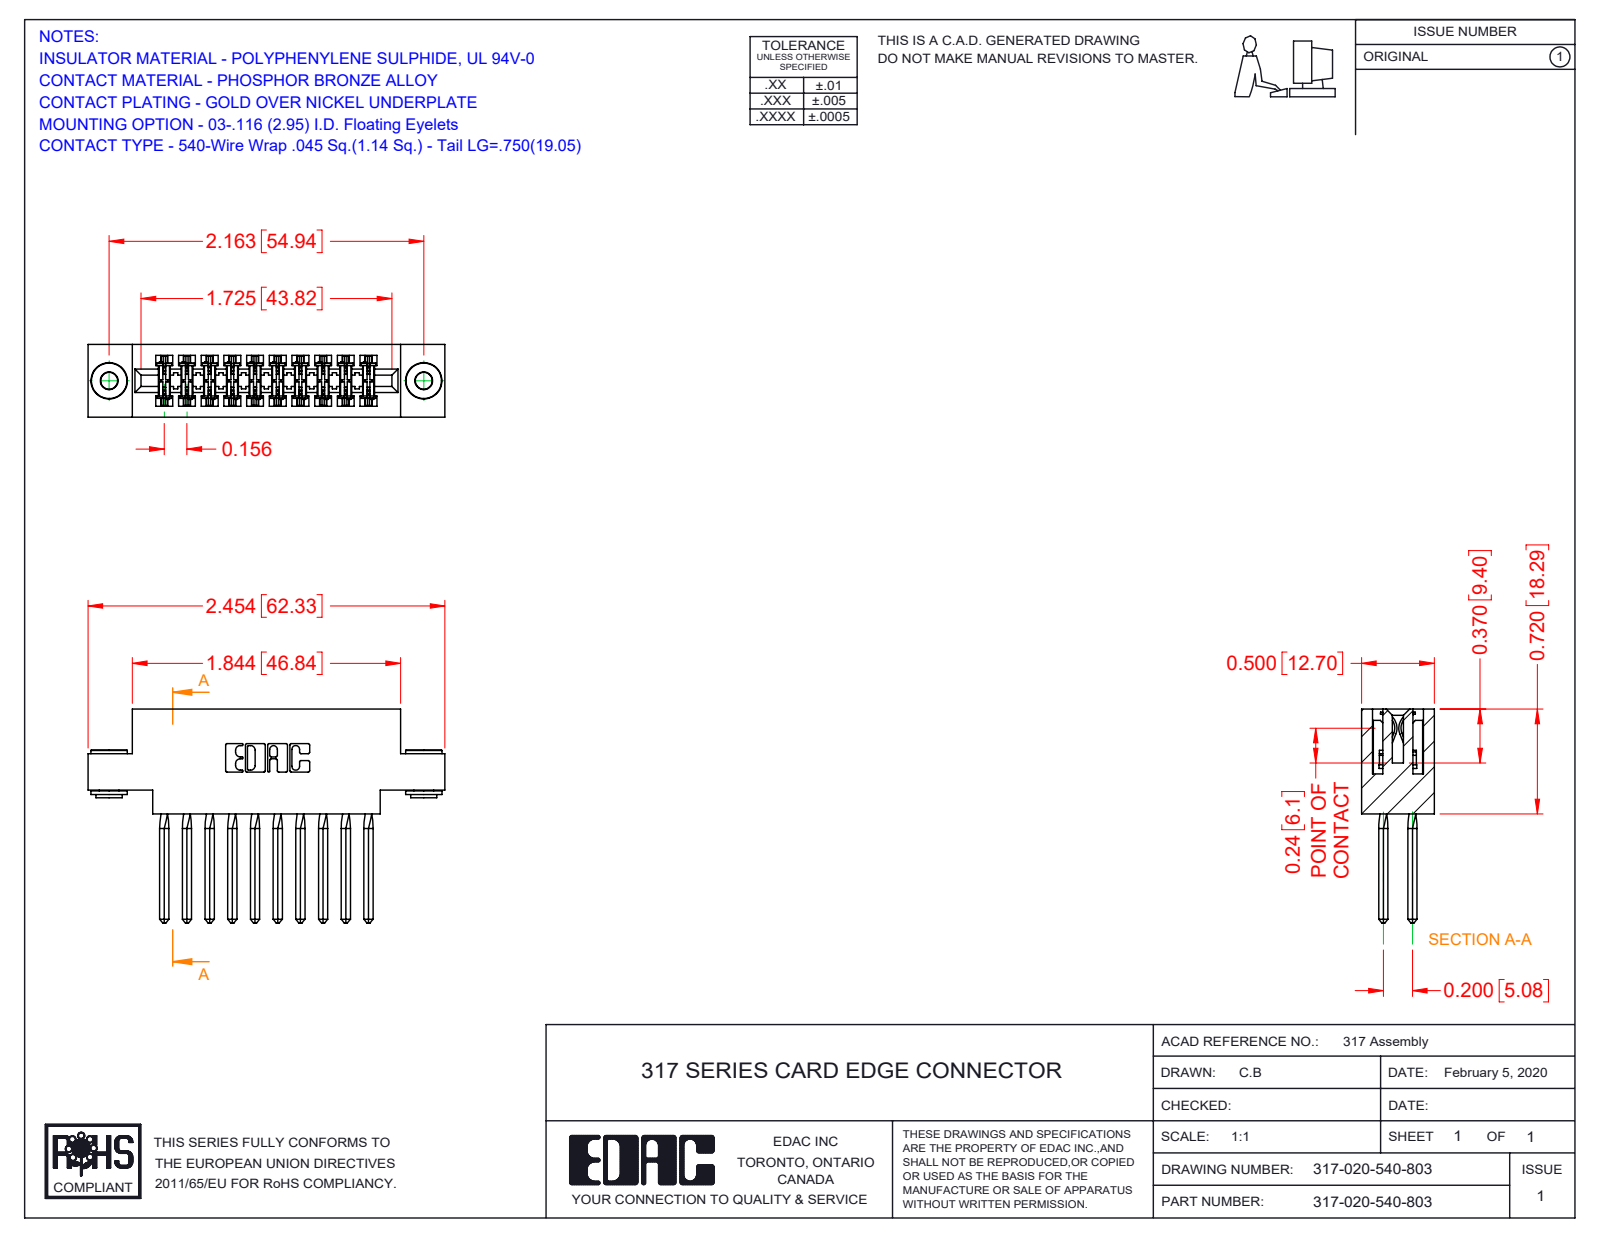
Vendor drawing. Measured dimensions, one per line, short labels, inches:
name: 317 Part_.156 Dia - TH; 317-020-540-803; 317-290-001_540; 345-250-002_345-250-002-102
written by: SolidWorks 2016 (CONFIG_CONTROL_DESIGN)
unit: in
bodies: 23 solids, 1920 faces (1528 planar, 304 cylindrical, 88 other)
size: 2.454 × 1.47 × 0.5
volume: 0.574 in³; area: 20.18 in²
holes: 2× ⌀0.116, 2× ⌀0.156
bosses: 2× ⌀0.25, 2× ⌀0.18, 2× ⌀0.136
rounds: 40× R0.015, 22× R0.01, 6× R0.007, 6× R0.031, 3× R0.026, 2× R0.095, 2× R0.1, 2× R0.11
face distances: 0.5, 0.075, 0.425, 0.11, 0.22, 0.35, 0.331, 0.156, 0.305, 0.116
hole spacings: 2.163
